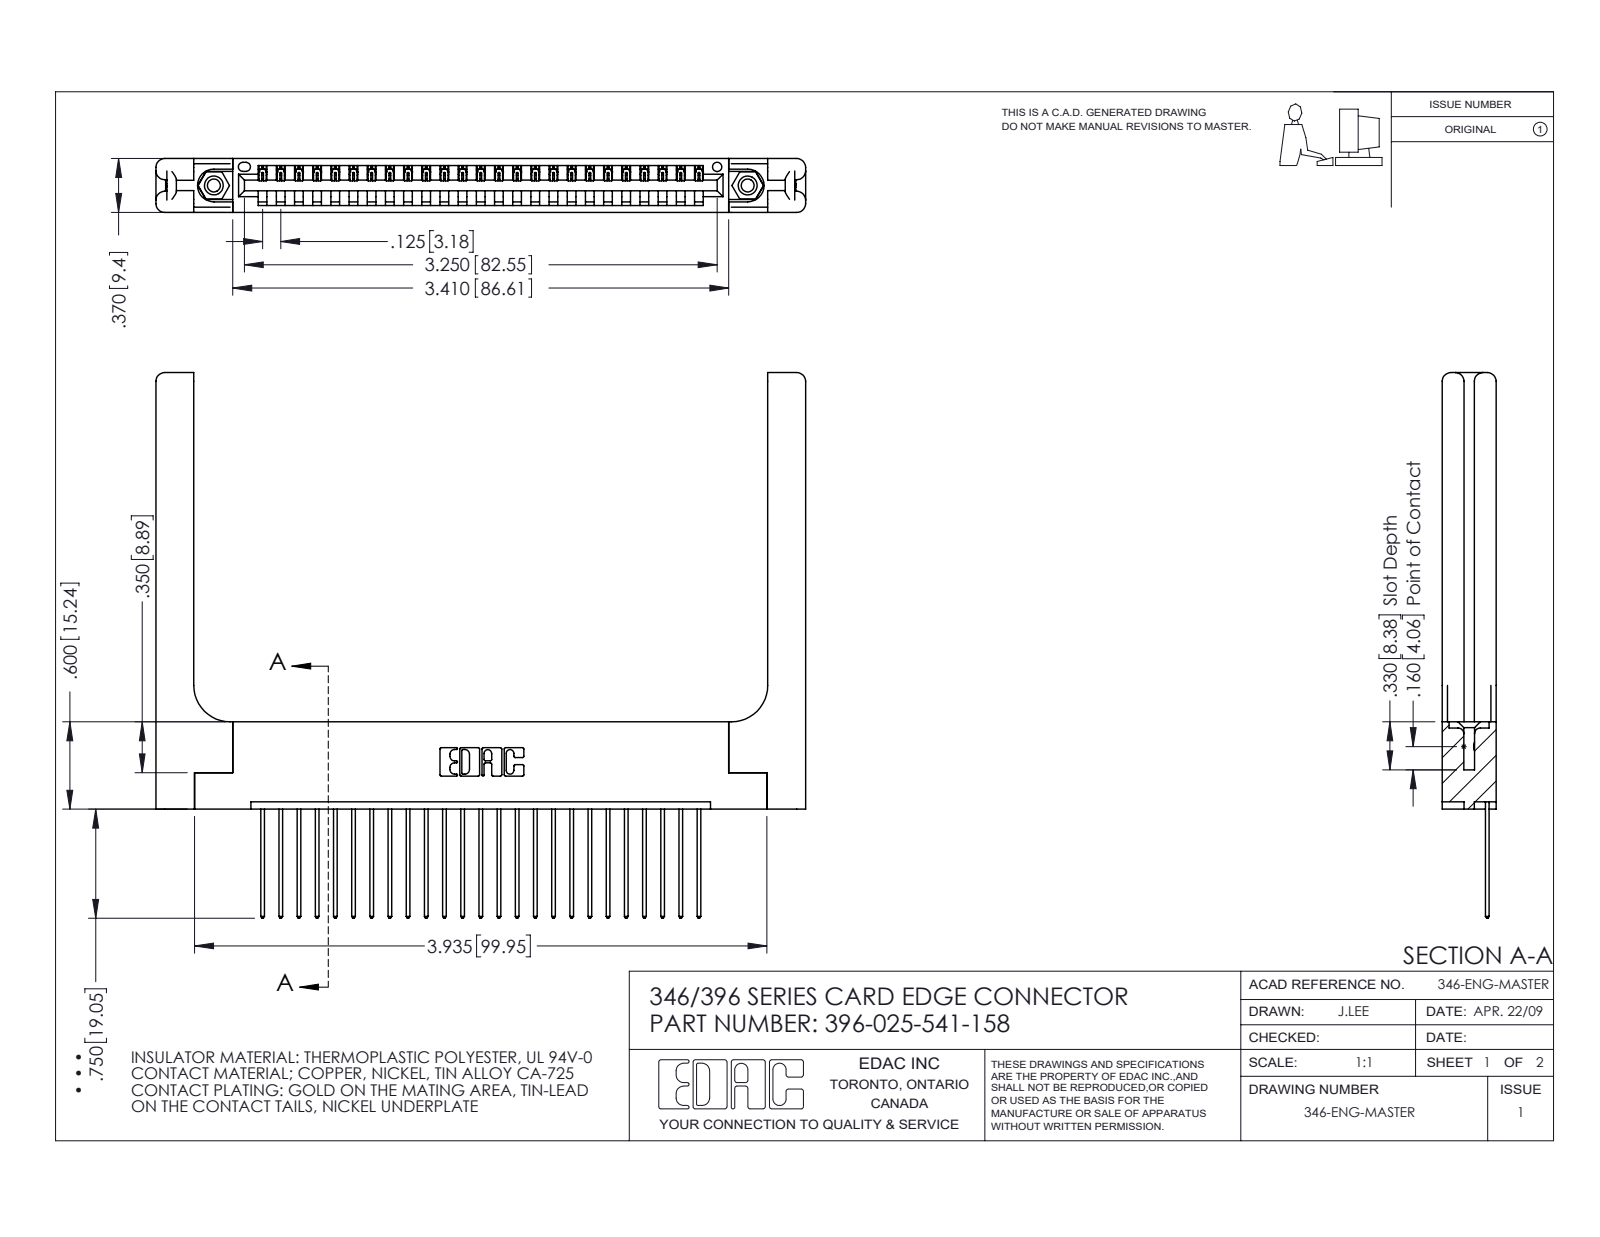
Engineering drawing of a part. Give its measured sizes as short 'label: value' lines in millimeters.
name: 345-292-001_345-293-141; 345-250-001_345-250-001-102; 346-220-058_345-220-058; 346 Part_Flush Mounting Lugs - 0.156 Dia-TH (+1 more)
written by: SolidWorks 2016 (CONFIG_CONTROL_DESIGN)
unit: mm
bodies: 30 solids, 1828 faces (1224 planar, 544 cylindrical, 60 other)
size: 113.4 × 95.3 × 9.4
volume: 18 340 mm³; area: 19 010 mm²
holes: 2× ⌀2.3, 2× ⌀3.2, 2× ⌀4, 1× ⌀1.6
bosses: 2× ⌀3.9
rounds: 50× R0.2, 50× R0.3, 22× R0.3, 16× R1.5, 6× R0.2, 6× R0.8, 3× R0.7, 2× R0.8
face distances: 9.4, 1.8, 1.2, 8.2, 3.8, 3.8, 6.4, 7.6, 0.6, 2
hole spacings: 6.2, 87.9, 93.2
